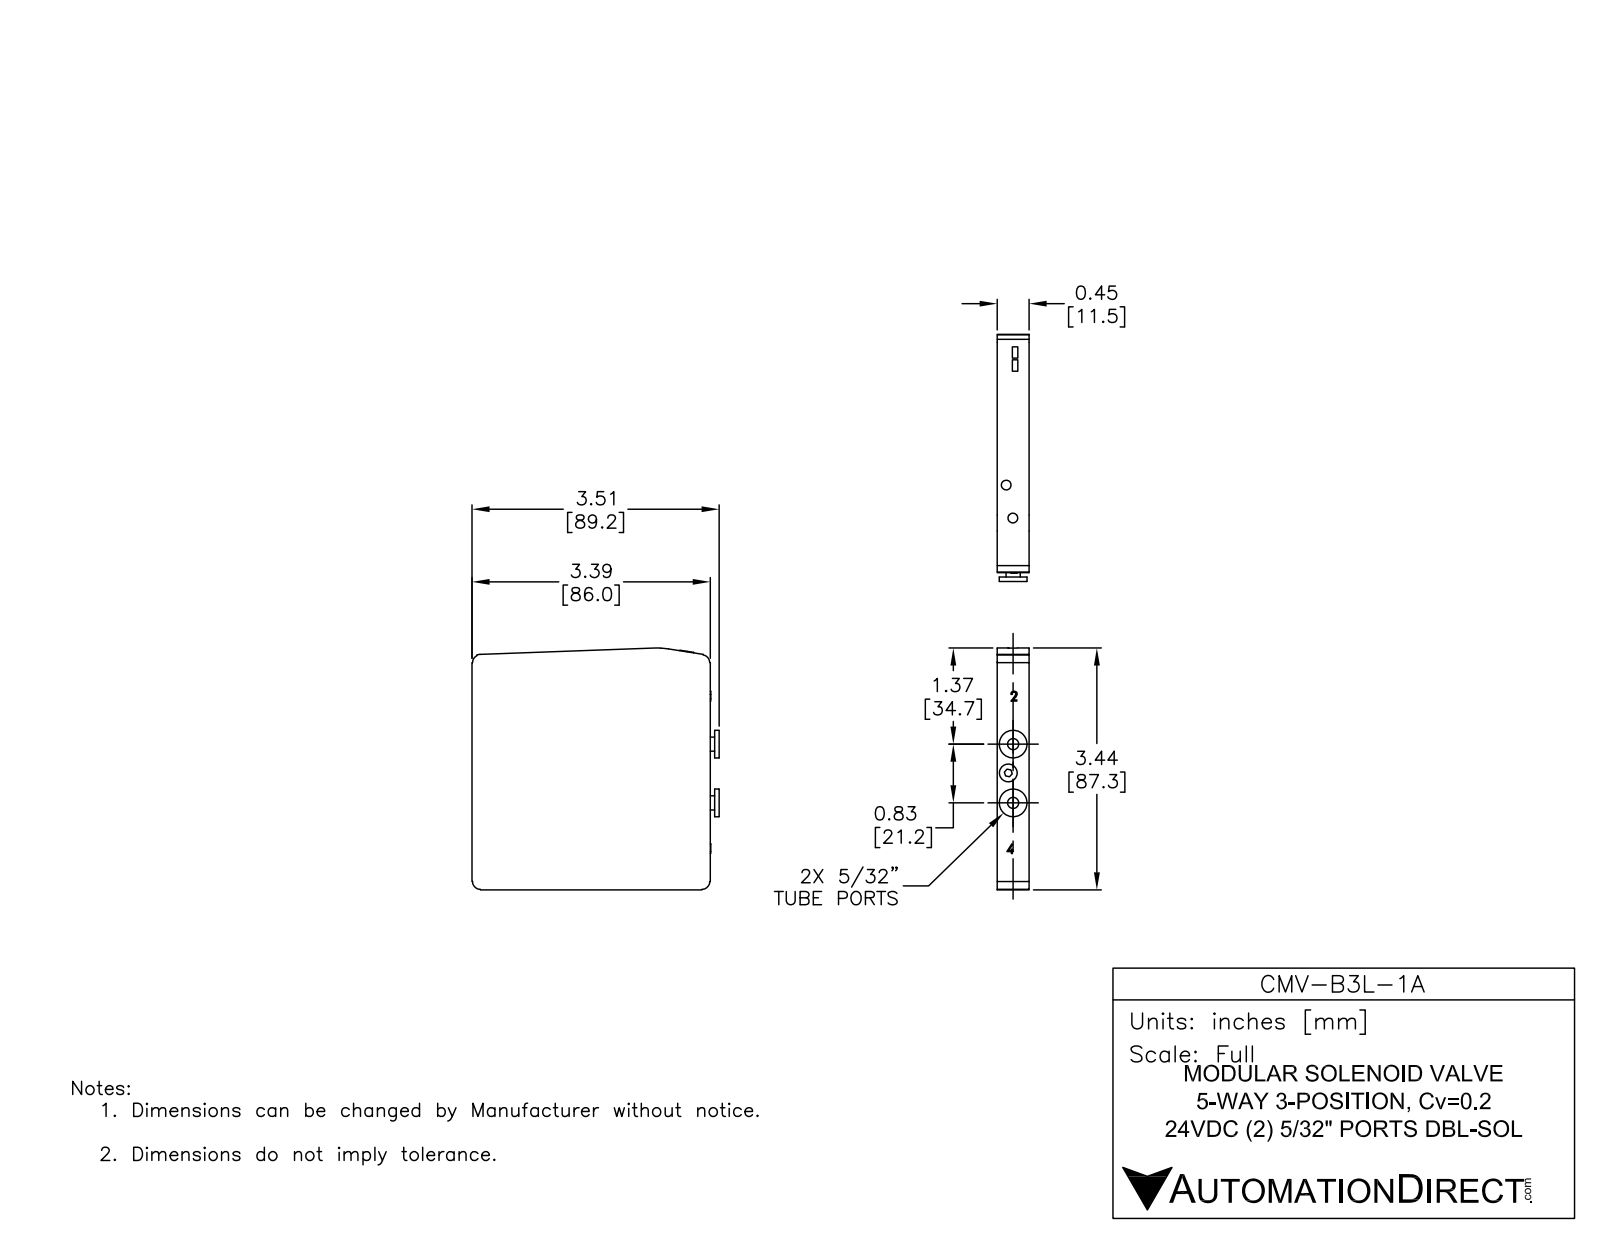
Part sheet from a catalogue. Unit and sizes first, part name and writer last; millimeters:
Units: millimetres
Overall size (bounding box): 89.5 × 87.3 × 20.43
Round holes (diameter × count): ⌀5.25 ×4, ⌀6.5 ×4, ⌀3.35 ×2, ⌀4.4 ×2, ⌀8 ×2, ⌀9.5 ×2, ⌀3.6 ×1, ⌀6.25 ×1, ⌀6.4 ×1
Round bosses / shafts (diameter × count): ⌀1.5 ×4, ⌀10.8 ×2, ⌀7.75 ×2, ⌀6.25 ×2, ⌀5.75 ×2, ⌀4.2 ×2, ⌀4 ×2, ⌀3.5 ×1
Partial cylindrical surfaces — rounded edges, fillets, slot ends (radius × count): R2.35 ×12, R0.78 ×4, R1.5 ×4, R2.8 ×4, R0.15 ×2, R0.25 ×2, R1 ×2, R2.25 ×2
Main face-to-face distances: 11.5, 1.5, 10, 1, 3, 83, 2.5, 12.5, 10.83, 11.83
Hole centre spacings: 9.7, 19.83, 22.17, 8.66, 8.68, 9.46, 10.38, 10.63
Volume: 78 069 mm³ · Surface area: 44 233 mm²
Bodies: 78 solids, 1151 faces (880 planar, 162 cylindrical, 109 other)
Part name (STEP PRODUCT): CMV-B3L-1A
STEP written by: SolidWorks 2013 (AUTOMOTIVE_DESIGN)
